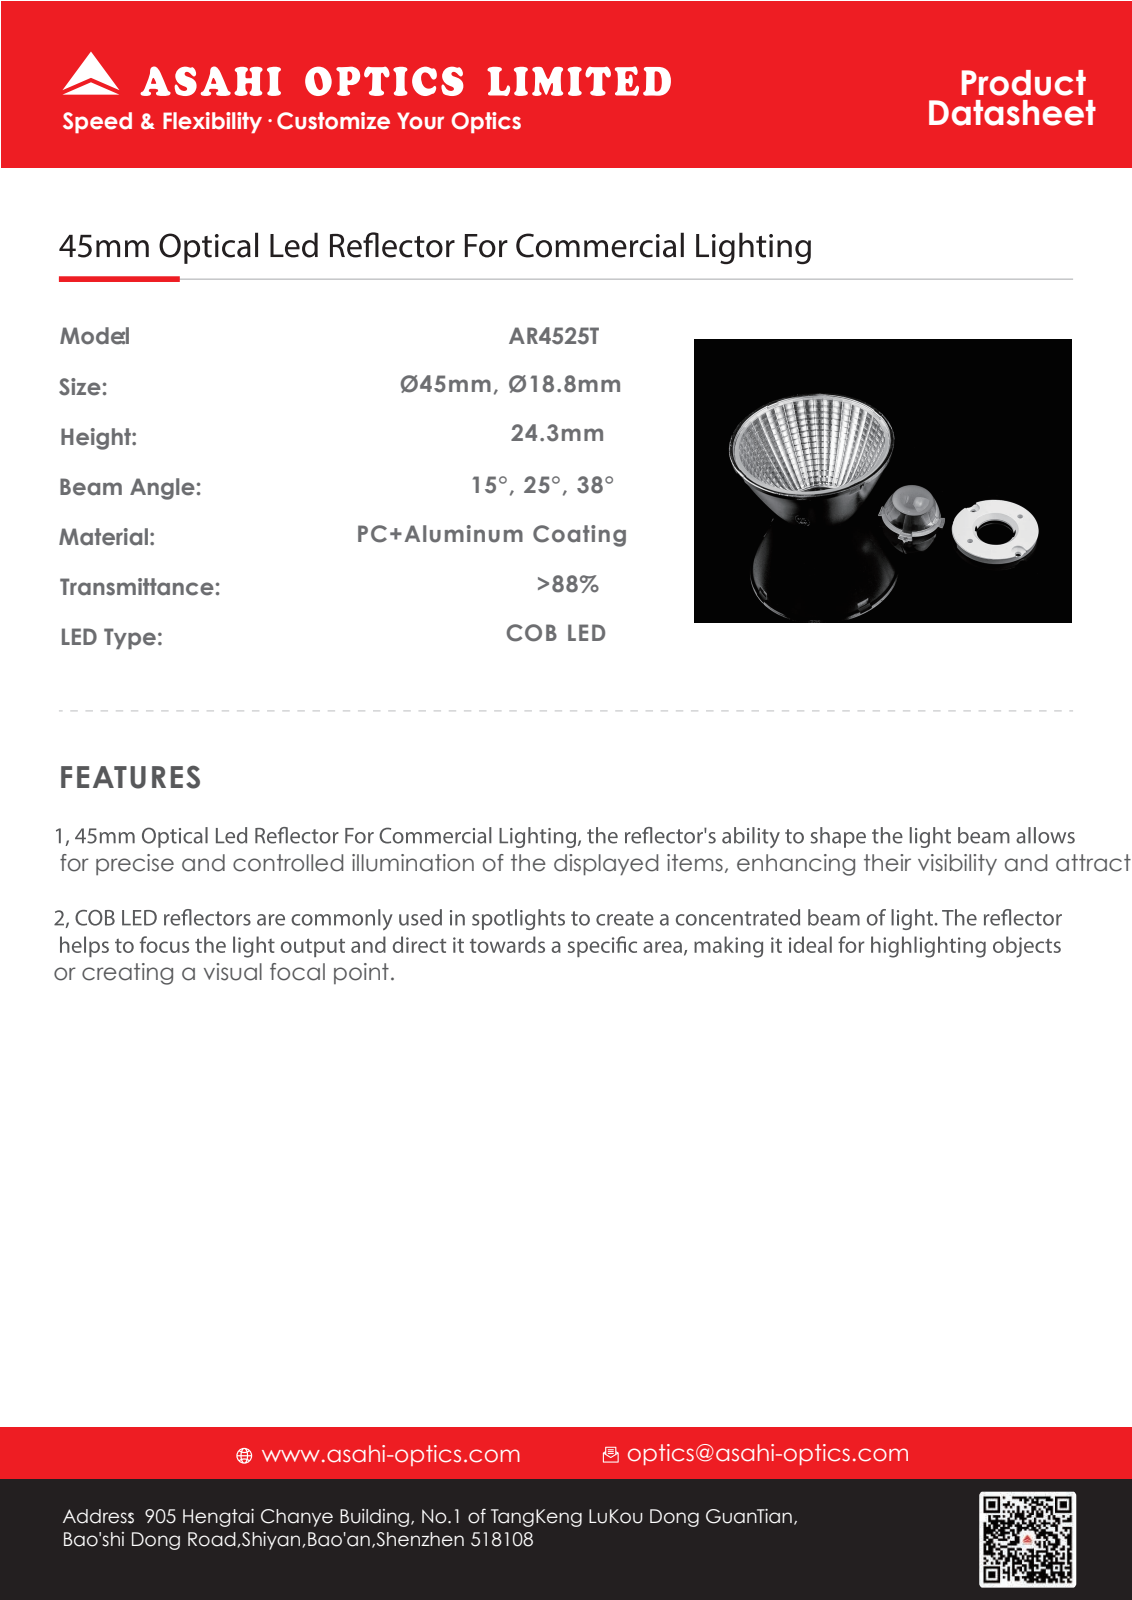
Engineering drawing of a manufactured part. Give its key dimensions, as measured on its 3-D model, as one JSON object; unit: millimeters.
{"part_name": "D4536-1205", "step_written_by": "SolidWorks 2014 (CONFIG_CONTROL_DESIGN)", "units": "millimeters", "bodies": {"solids": 1, "faces": 126, "planar": 27, "cylindrical": 11, "other": 88}, "overall_size": [45, 45, 24.3], "volume_mm3": 2254, "surface_area_mm2": 6272, "round_holes": [[42.3, 1]], "round_bosses_or_shafts": [[45, 1]], "partial_cylinders_radius": [[20.6, 1]], "face_to_face_distances": [2.71, 21.59, 24.3, 22.57, 0.98, 1.73, 23.62, 2.03, 1.05, 0.68]}
